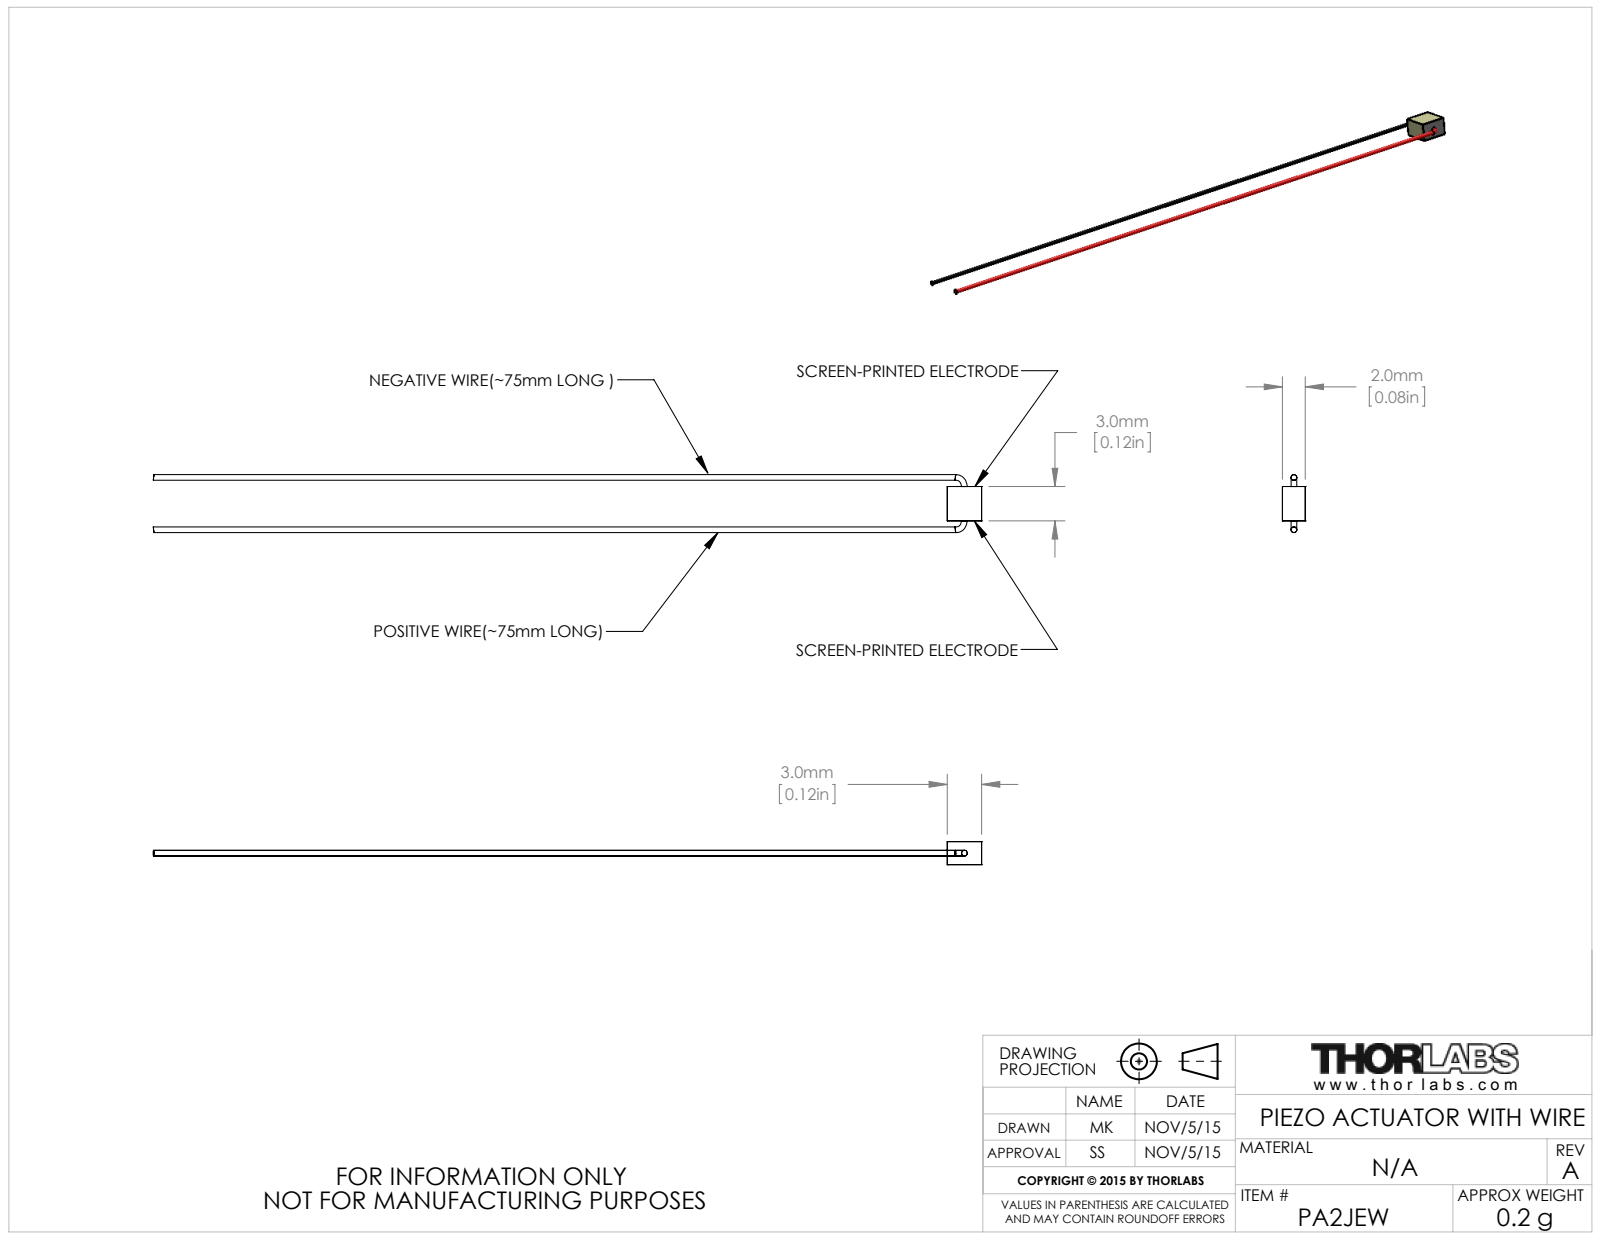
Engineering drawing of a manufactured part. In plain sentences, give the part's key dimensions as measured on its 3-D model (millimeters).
The part is named "CTN003182". Its 3-D file was written by "SolidWorks 2014 (AUTOMOTIVE_DESIGN)". It is 1 solid with 16 faces: 8 planar, 0 cylindrical and 8 other. Overall it measures 72.33 by 5.06 by 2 millimeters. Its volume is 46 cubic millimeters and its surface area 265 square millimeters. The main face-to-face distances are 3, 2.
